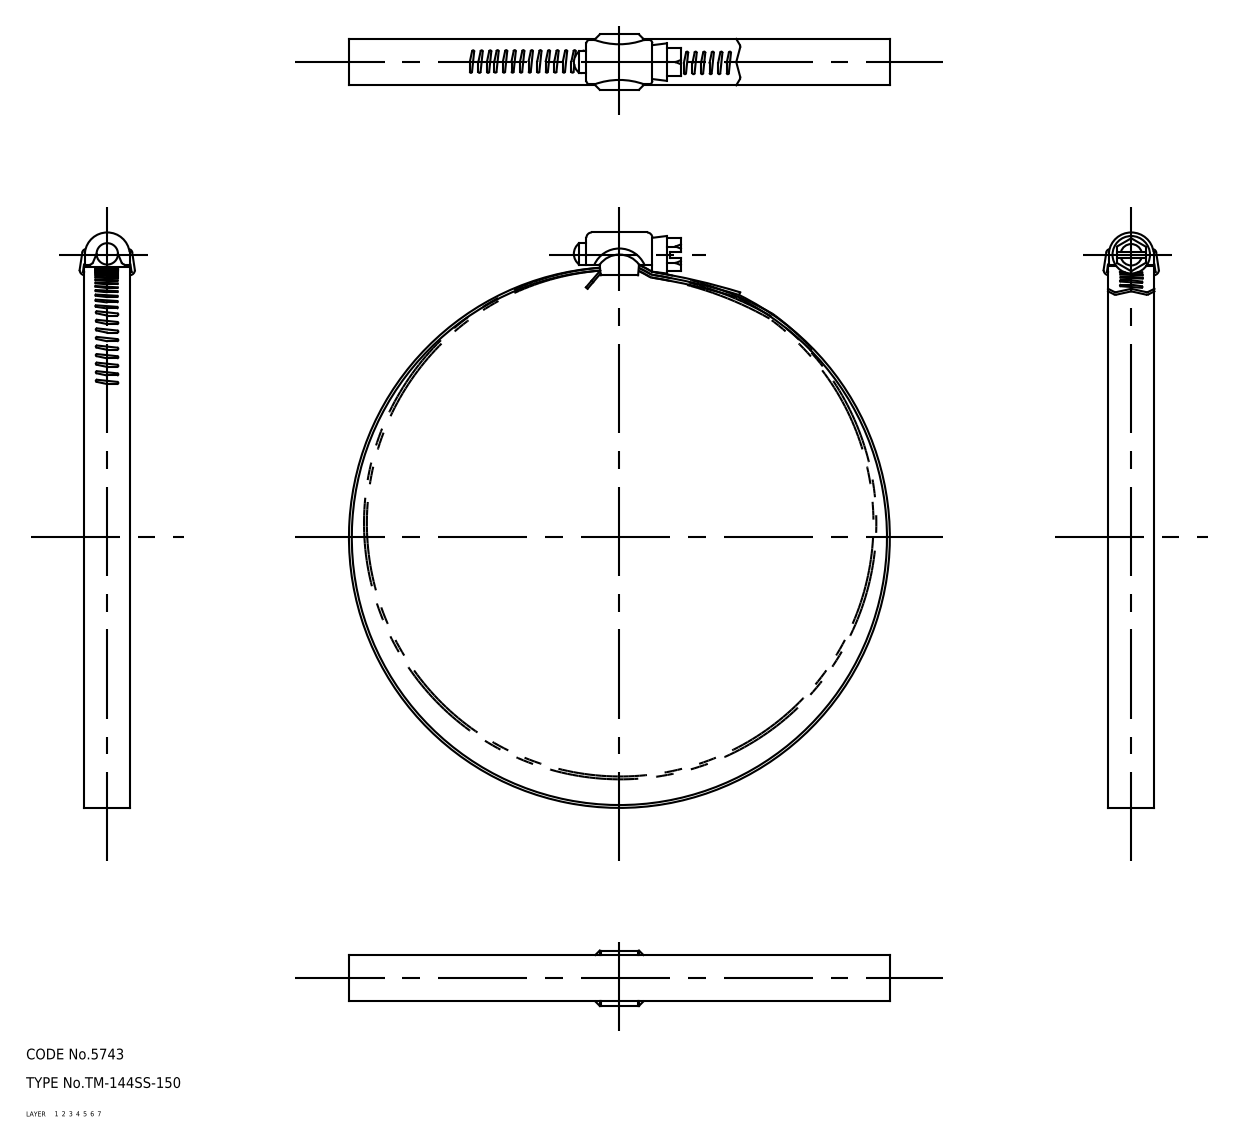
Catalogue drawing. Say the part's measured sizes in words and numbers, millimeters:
The part is named "screw; holder; band; TM_144SS_150_19521_36". Its 3-D file was written by "CADfix (AUTOMOTIVE_DESIGN)". It is 3 solids with 216 faces: 0 planar, 0 cylindrical and 216 other. Overall it measures 161.29 by 151.6 by 15.63 millimeters. Its volume is 7 503 cubic millimeters and its surface area 16 546 square millimeters.
